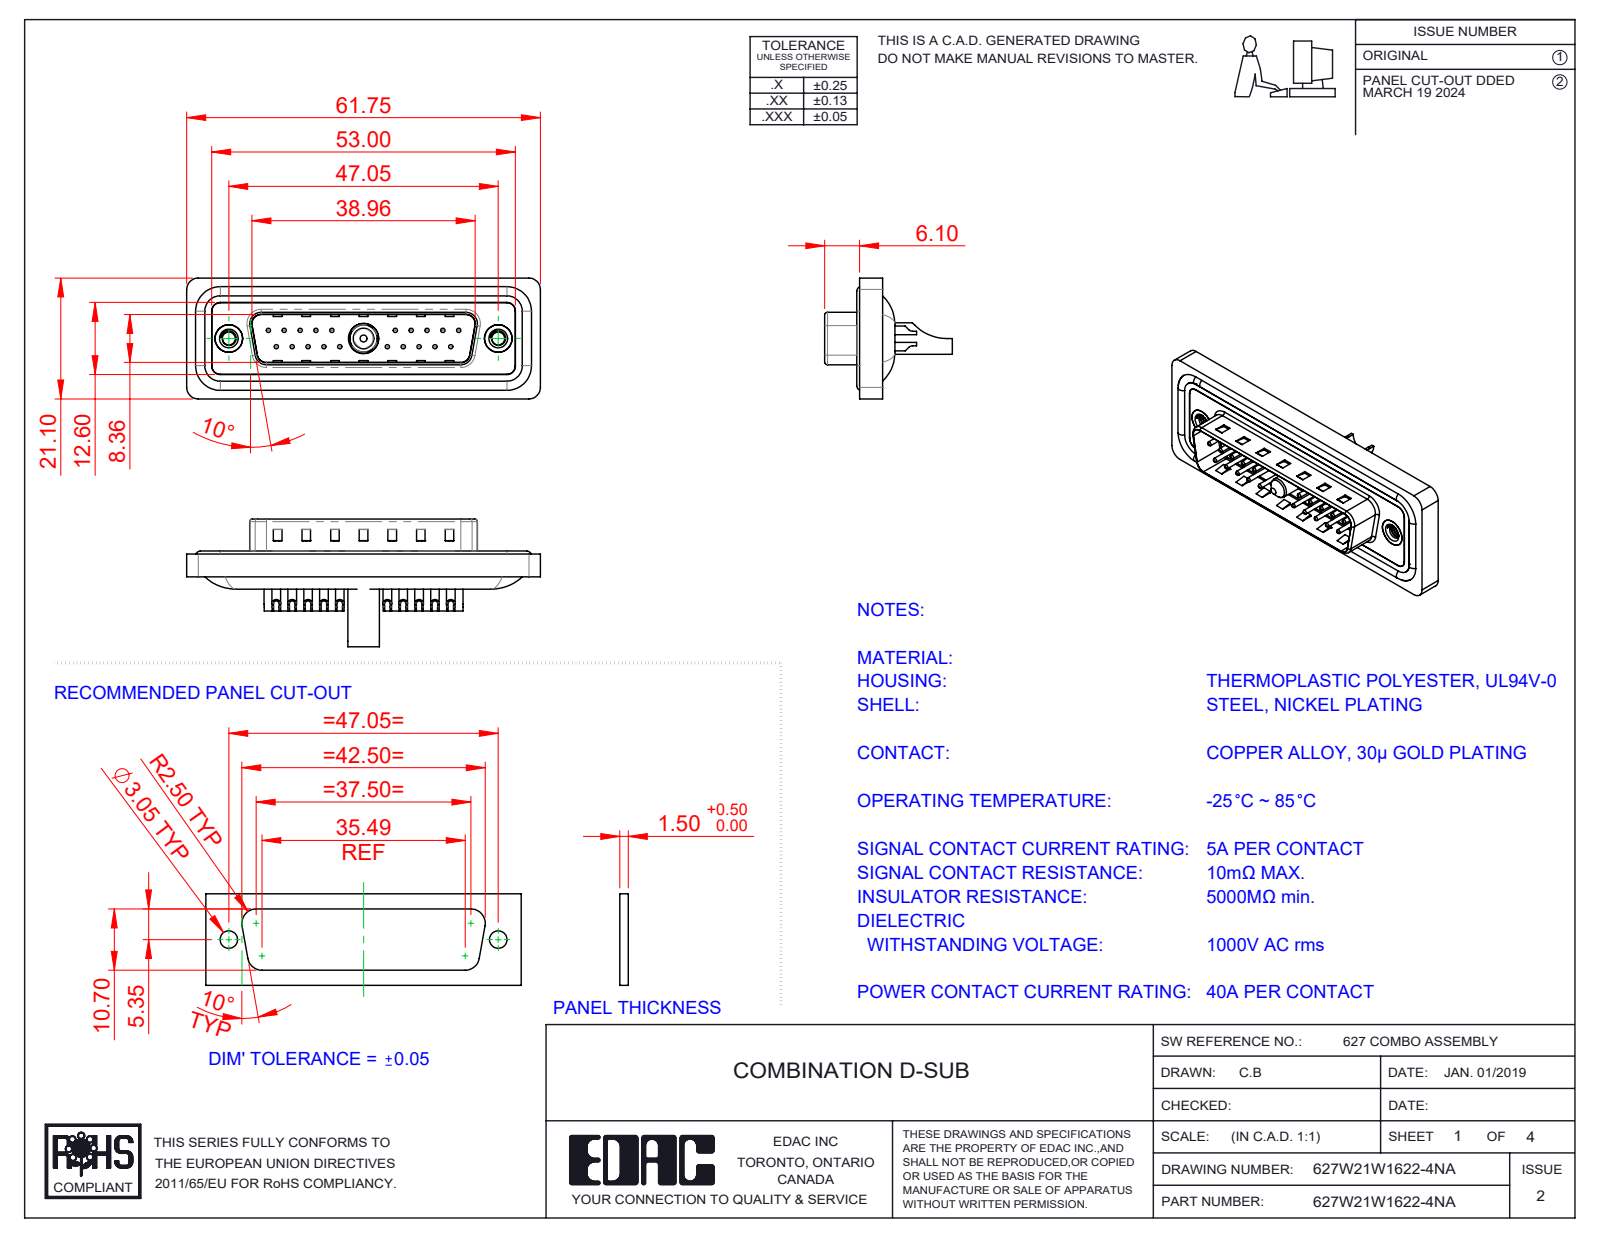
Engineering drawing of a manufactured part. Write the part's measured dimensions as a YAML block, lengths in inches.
part_name: "627Combo Contact Row 1_22; 627W21W1622-4NA; 627Combo Waterproof Housing_25 Contacts; 627Combo Housing_21W1 (+5 more)"
step_written_by: "SolidWorks 2023 (CONFIG_CONTROL_DESIGN)"
units: inches
bodies: {solids: 29, faces: 1264, planar: 401, cylindrical: 530, other: 333}
overall_size: [2.431, 0.878, 0.831]
volume: 0.444
surface_area: 18.99
round_holes:
  - {diameter: 0.03, count: 20}
  - {diameter: 0.039, count: 20}
  - {diameter: 0.063, count: 20}
  - {diameter: 0.079, count: 20}
  - {diameter: 0.089, count: 2}
  - {diameter: 0.157, count: 2}
  - {diameter: 0.189, count: 2}
  - {diameter: 0.197, count: 2}
  - {diameter: 0.181, count: 1}
  - {diameter: 0.191, count: 1}
  - {diameter: 0.209, count: 1}
round_bosses_or_shafts:
  - {diameter: 0.059, count: 20}
  - {diameter: 0.063, count: 4}
  - {diameter: 0.193, count: 2}
  - {diameter: 0.217, count: 1}
  - {diameter: 0.205, count: 1}
  - {diameter: 0.187, count: 1}
  - {diameter: 0.148, count: 1}
  - {diameter: 0.142, count: 1}
partial_cylinders:
  - {radius: 0.059, count: 22}
  - {radius: 0.079, count: 18}
  - {radius: 0.02, count: 8}
  - {radius: 0.063, count: 8}
  - {radius: 0.039, count: 6}
  - {radius: 0.01, count: 4}
  - {radius: 0.024, count: 4}
  - {radius: 0.026, count: 4}
face_to_face_distances: [0.016, 0.059, 0.043, 0.063, 0.02, 0.122, 0.114, 0.161, 0.032, 0.377]
hole_center_spacings: [0.124, 0.109, 0.218, 0.327, 0.198, 0.763, 0.826, 0.872]
